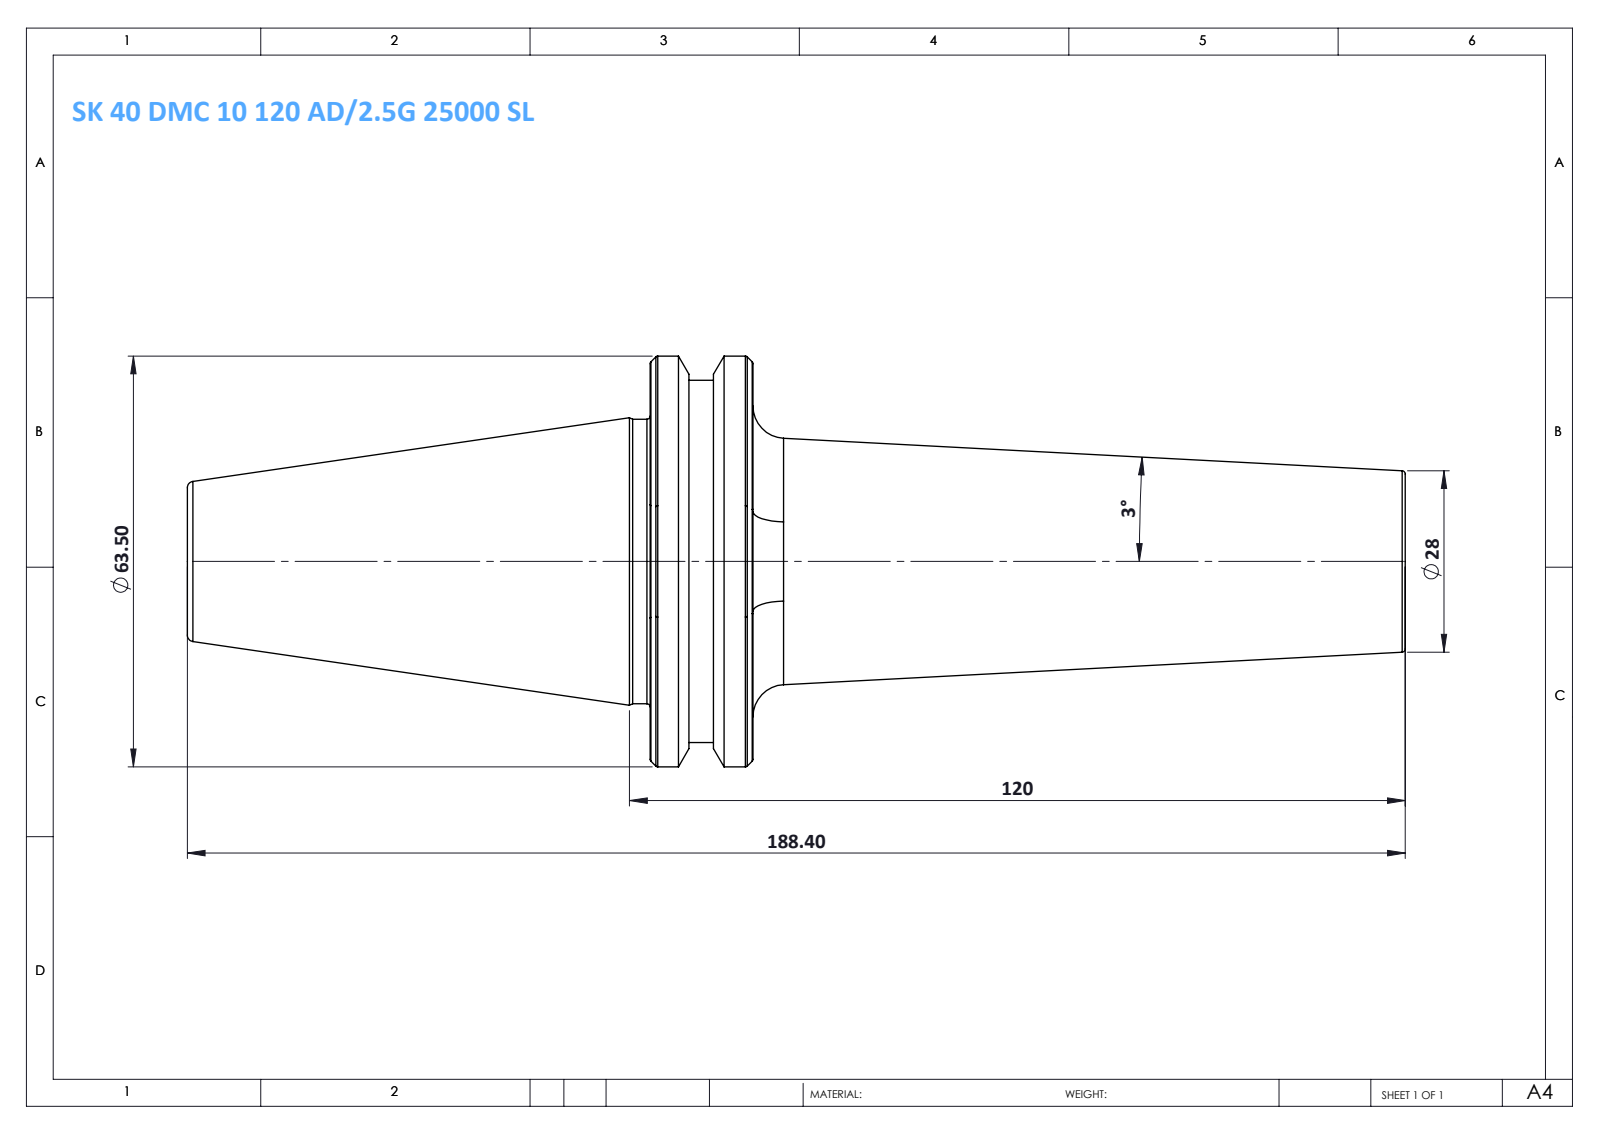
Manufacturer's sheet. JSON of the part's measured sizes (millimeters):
{"part_name": "SK 40 DMC 10 120 AD-2.5G 25000 SL", "step_written_by": "SolidWorks 2014 (CONFIG_CONTROL_DESIGN)", "units": "millimeters", "bodies": {"solids": 1, "faces": 66, "planar": 6, "cylindrical": 8, "other": 52}, "overall_size": [188.4, 63.5, 63.5], "volume_mm3": 206255, "surface_area_mm2": 26704, "round_bosses_or_shafts": [[63.5, 1], [56, 1], [44, 1]], "face_to_face_distances": [15.9, 100.9, 116.8, 188.4, 87.5, 71.6, 107, 6.1, 9.8, 81.4]}
